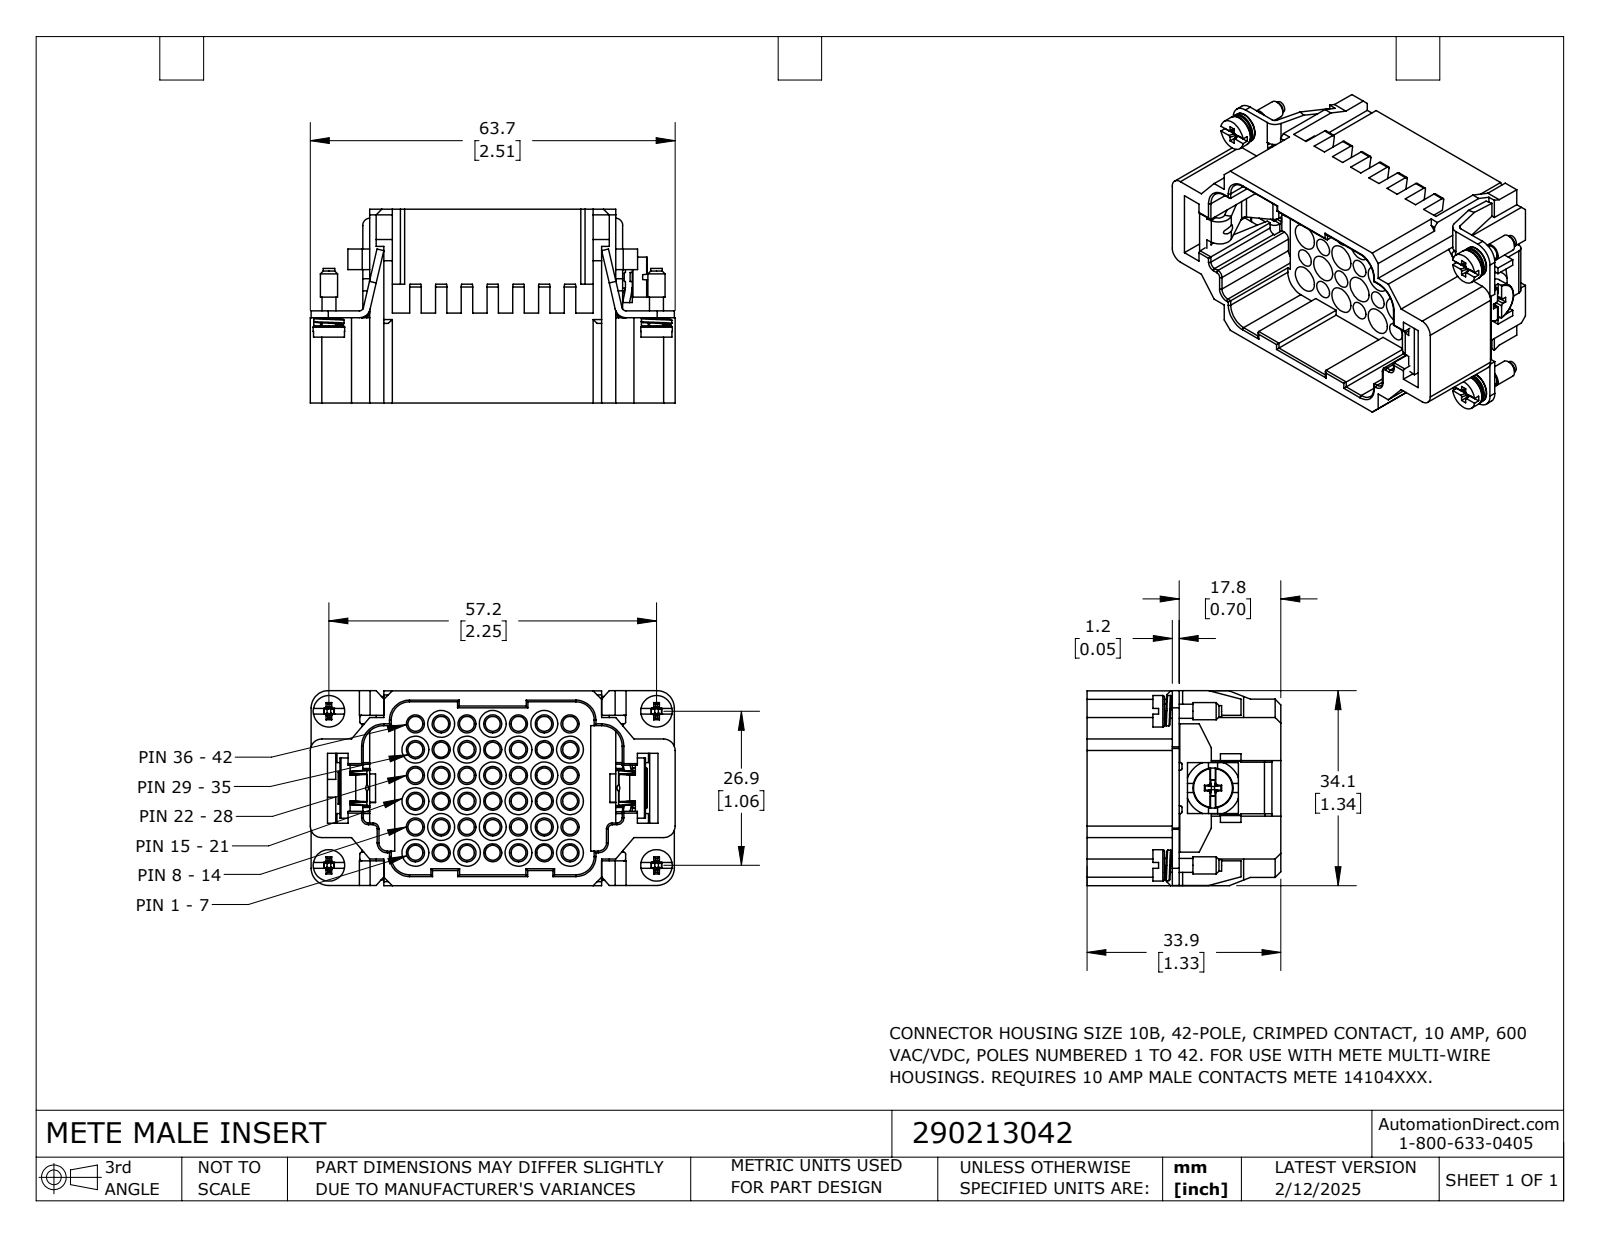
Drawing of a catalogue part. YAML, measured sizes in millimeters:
part_name: "290213042"
step_written_by: "SolidWorks 2024 (CONFIG_CONTROL_DESIGN)"
units: millimeters
bodies: {solids: 13, faces: 1592, planar: 781, cylindrical: 720, other: 91}
overall_size: [63.7, 34.1, 33.9]
volume: 22110
surface_area: 26800
round_holes:
  - {diameter: 2.6, count: 42}
  - {diameter: 3.1, count: 42}
  - {diameter: 3.5, count: 42}
  - {diameter: 3.8, count: 42}
  - {diameter: 4.7, count: 21}
  - {diameter: 2.9, count: 4}
  - {diameter: 3.3, count: 1}
round_bosses_or_shafts:
  - {diameter: 5.5, count: 4}
  - {diameter: 5.3, count: 4}
  - {diameter: 3, count: 4}
  - {diameter: 2.4, count: 4}
  - {diameter: 2, count: 4}
  - {diameter: 7, count: 1}
  - {diameter: 5, count: 1}
  - {diameter: 3.9, count: 1}
partial_cylinders:
  - {radius: 0.3, count: 33}
  - {radius: 0.3, count: 32}
  - {radius: 0.1, count: 10}
  - {radius: 0.5, count: 10}
  - {radius: 1.3, count: 10}
  - {radius: 0.2, count: 8}
  - {radius: 1.3, count: 8}
  - {radius: 2, count: 6}
face_to_face_distances: [1.2, 31.1, 2.9, 2, 2.5, 34, 38.5, 4.5, 0.5, 1.7]
hole_center_spacings: [10.1, 4.5, 14.2, 6.4, 9, 16.2, 18.5, 22.5]
